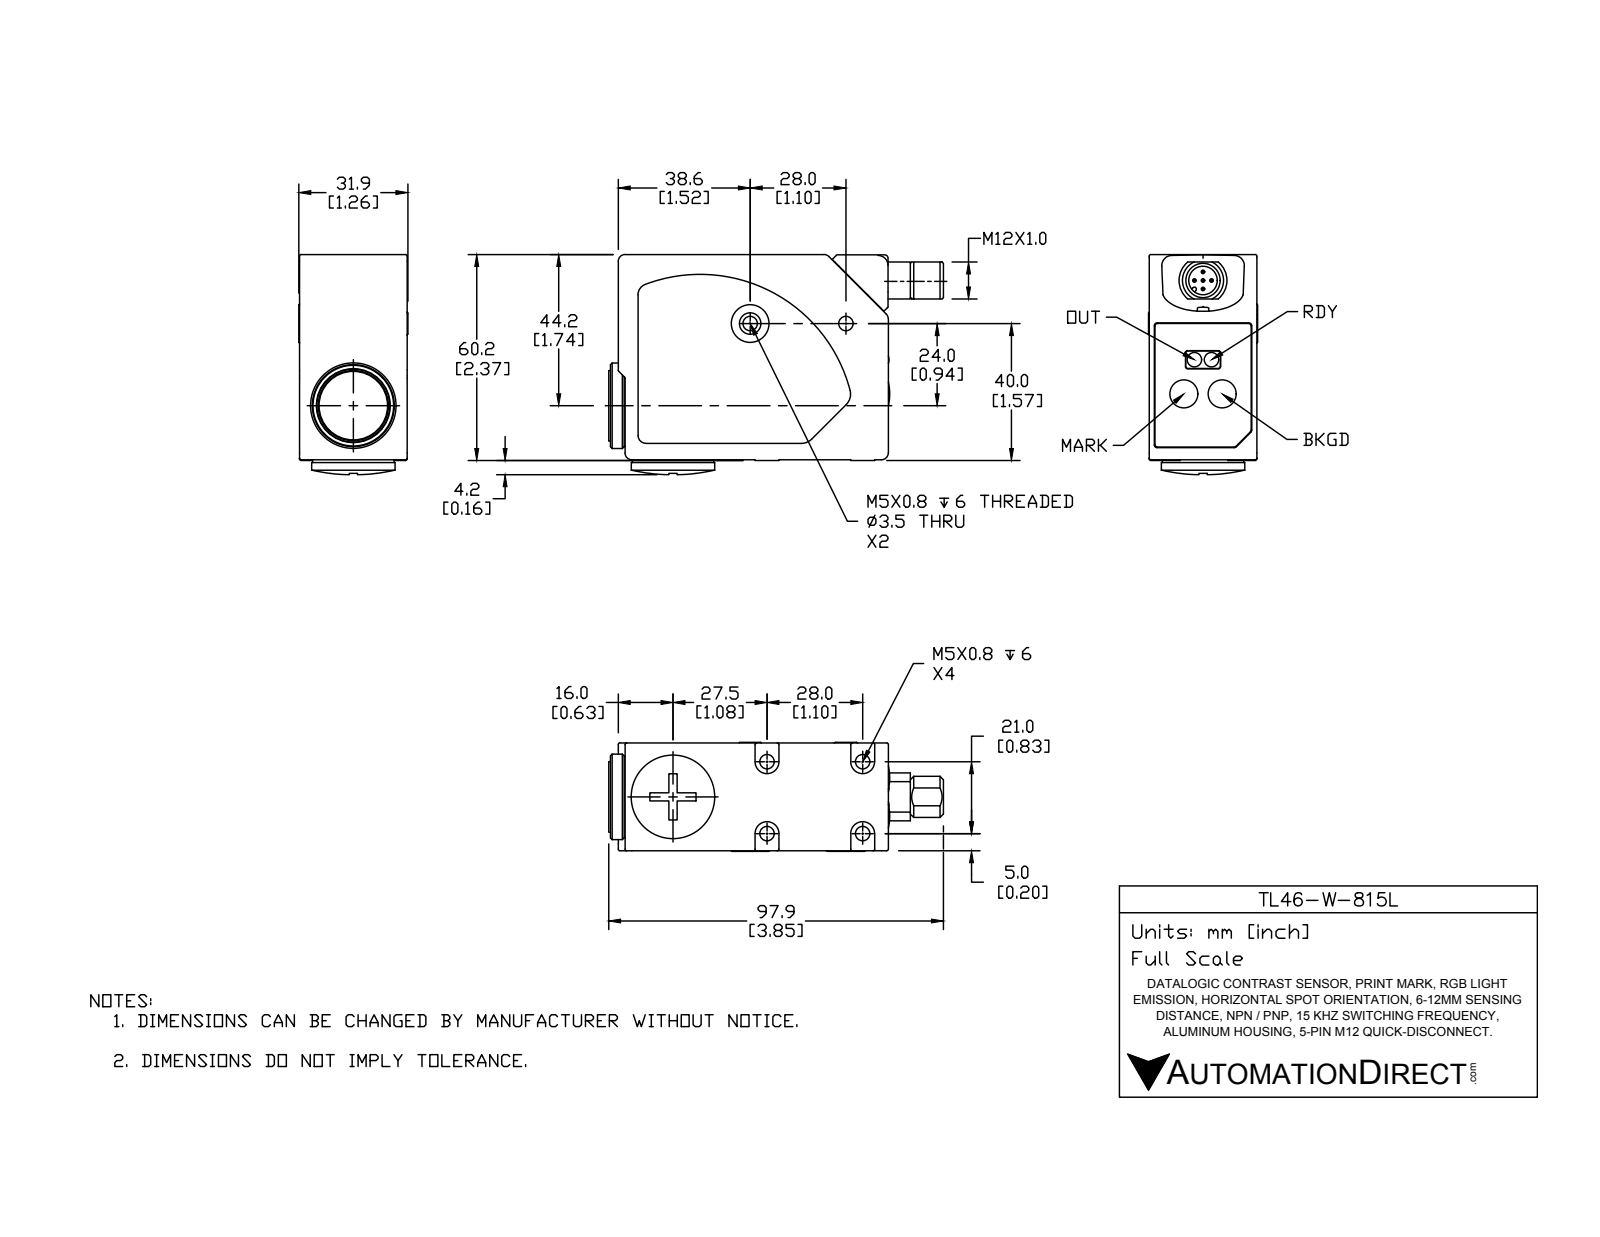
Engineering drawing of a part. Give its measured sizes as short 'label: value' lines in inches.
name: TL46-W-815L
written by: SolidWorks 2016 (AUTOMOTIVE_DESIGN)
unit: in
bodies: 7 solids, 332 faces (96 planar, 128 cylindrical, 108 other)
size: 3.854 × 2.534 × 1.256
volume: 9.069 in³; area: 33.48 in²
holes: 8× ⌀0.165, 2× ⌀0.323, 1× ⌀0.327, 1× ⌀0.787
bosses: 5× ⌀0.039, 2× ⌀0.937, 1× ⌀0.984, 1× ⌀0.961, 1× ⌀0.748, 1× ⌀0.433
rounds: 32× R0.02, 10× R0.031, 5× R0.024, 5× R0.079, 4× R0.02, 4× R0.138, 1× R0.236, 1× R0.276
face distances: 1.232, 1.224, 1.24, 2.362, 3.11, 3.031, 0.079, 0.016, 1.248, 2.37
hole spacings: 1.102, 0.259, 0.412, 0.507, 0.539, 0.827, 0.917, 1.324
